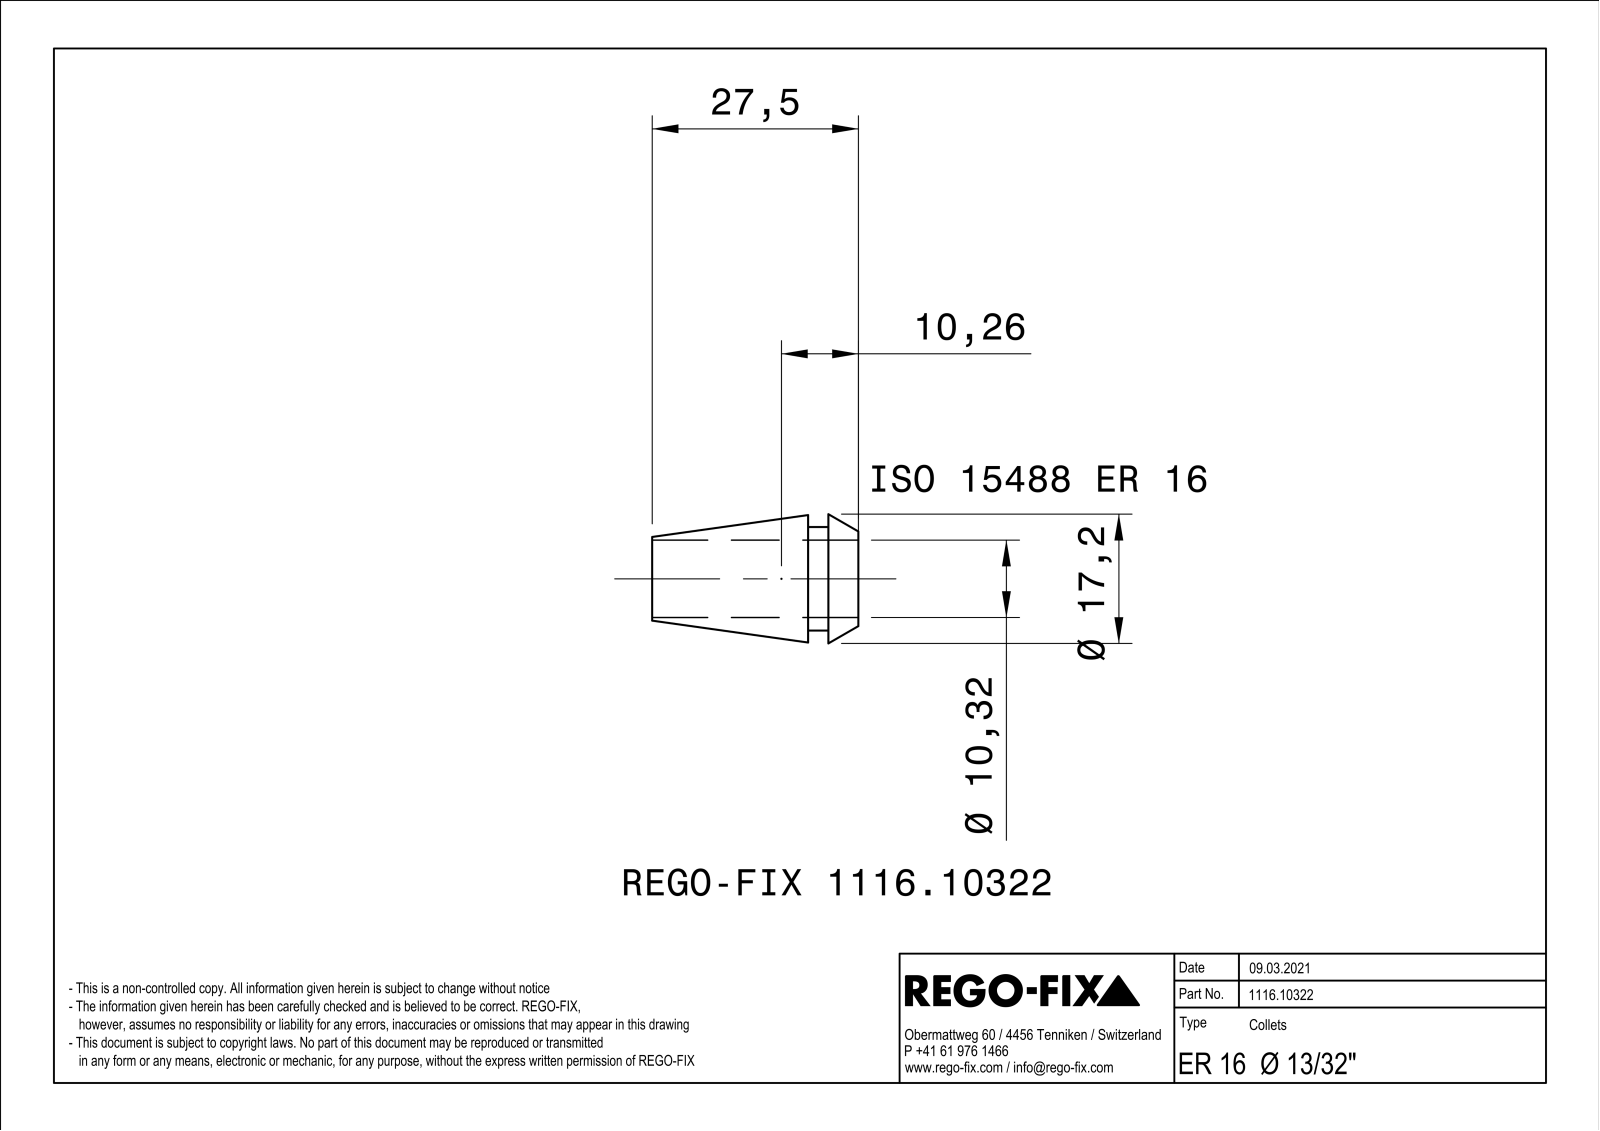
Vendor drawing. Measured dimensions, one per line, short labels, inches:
name: NOCUT
written by: SIEMENS PLM Software Solid Edge ST10 (AUTOMOTIVE_DESIGN)
unit: in
bodies: 1 solid, 153 faces (72 planar, 25 cylindrical, 56 other)
size: 1.083 × 0.679 × 0.679
volume: 0.1 in³; area: 5.244 in²
holes: 1× ⌀0.406
bosses: 1× ⌀0.543
rounds: 8× R0.012
face distances: 0.024, 0.106, 0.157, 0.264, 1.083, 0.925, 0.819
